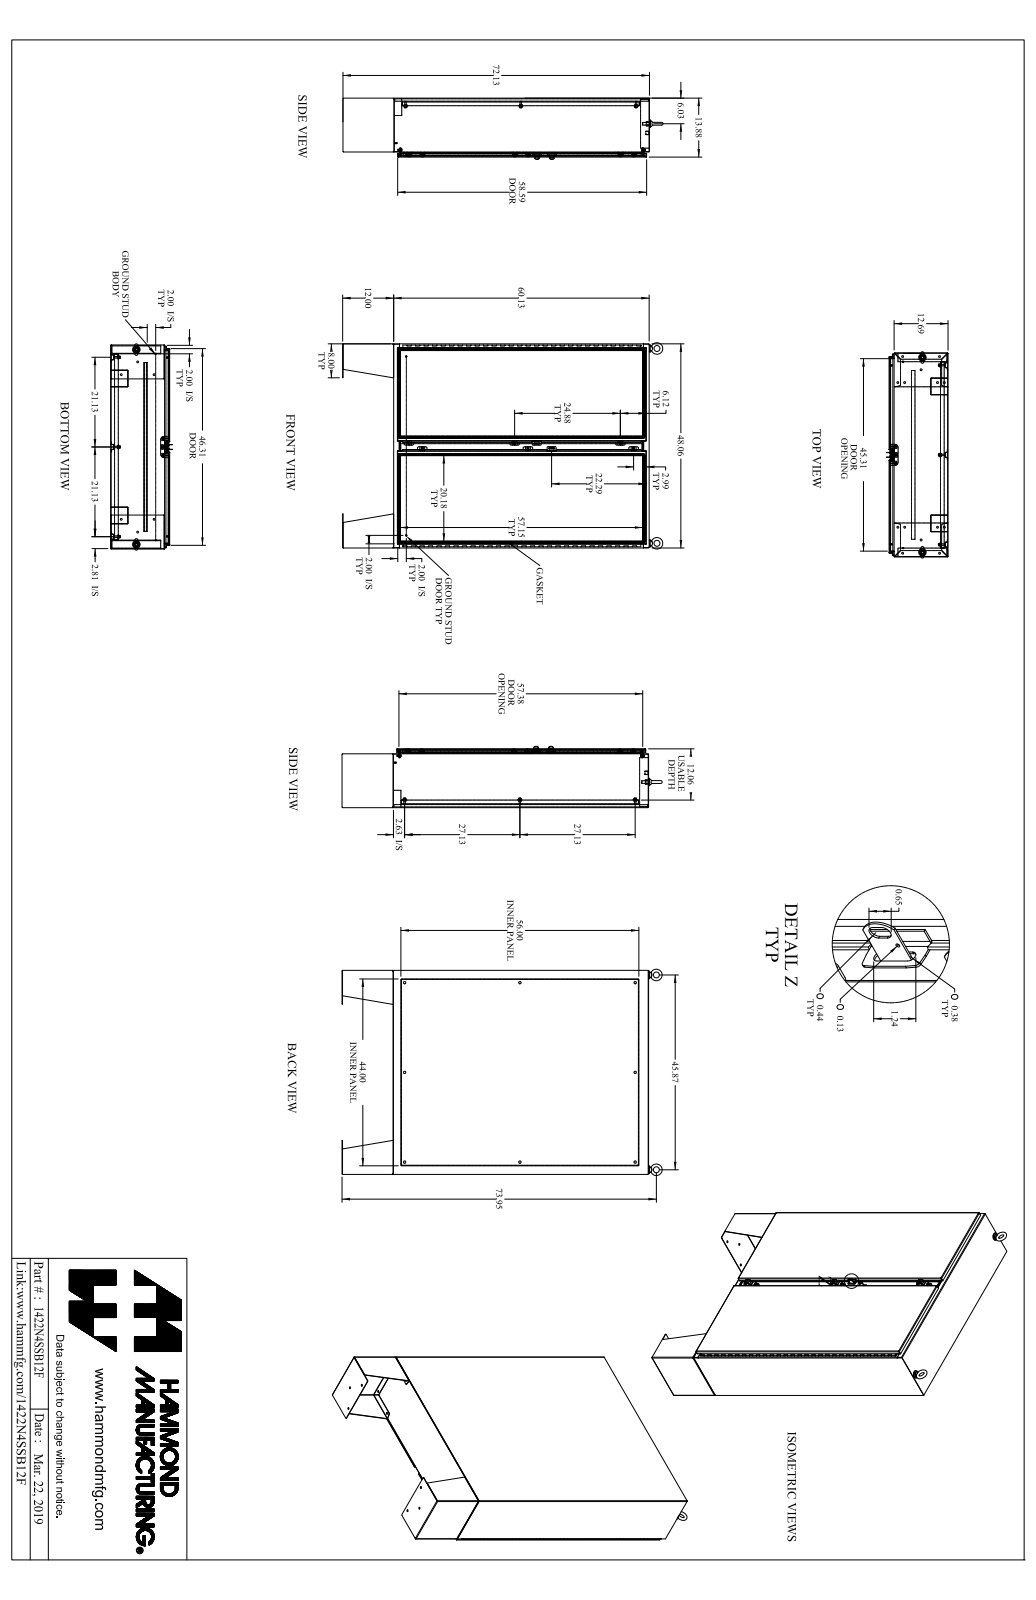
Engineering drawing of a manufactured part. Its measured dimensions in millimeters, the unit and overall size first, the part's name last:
Units: millimetres
Overall size (bounding box): 1924.9 × 1247.7 × 367.5
Round holes (diameter × count): ⌀7.7 ×20, ⌀11.1 ×14, ⌀7.8 ×8, ⌀14.3 ×8, ⌀5.4 ×6, ⌀6.7 ×6, ⌀9.5 ×6, ⌀11.3 ×6, ⌀5.1 ×3, ⌀6.4 ×3, ⌀8 ×3, ⌀2.8 ×2
Round bosses / shafts (diameter × count): ⌀25.4 ×8, ⌀16.5 ×8, ⌀9.5 ×8, ⌀8.4 ×8, ⌀12.7 ×6, ⌀9.9 ×6, ⌀6.2 ×6, ⌀8 ×4
Partial cylindrical surfaces — rounded edges, fillets, slot ends (radius × count): R1.2 ×67, R3.6 ×67, R6.4 ×34, R1.5 ×18, R2.9 ×12, R3.6 ×12, R4.7 ×12, R4.7 ×9
Main face-to-face distances: 2.4, 350, 347.6, 304.7, 3.2, 352.4, 307.2, 42.8, 45.3, 310.3
Hole centre spacings: 152.4, 1183.5, 304.8, 1212.5, 457.2, 1259.5, 609.6, 1322.5
Volume: 23 430 000 mm³ · Surface area: 18 690 000 mm²
Bodies: 107 solids, 3390 faces (1754 planar, 1440 cylindrical, 196 other)
Part name (STEP PRODUCT): 1422N4SSB12F_Default
STEP written by: SolidWorks 2019 (CONFIG_CONTROL_DESIGN)
